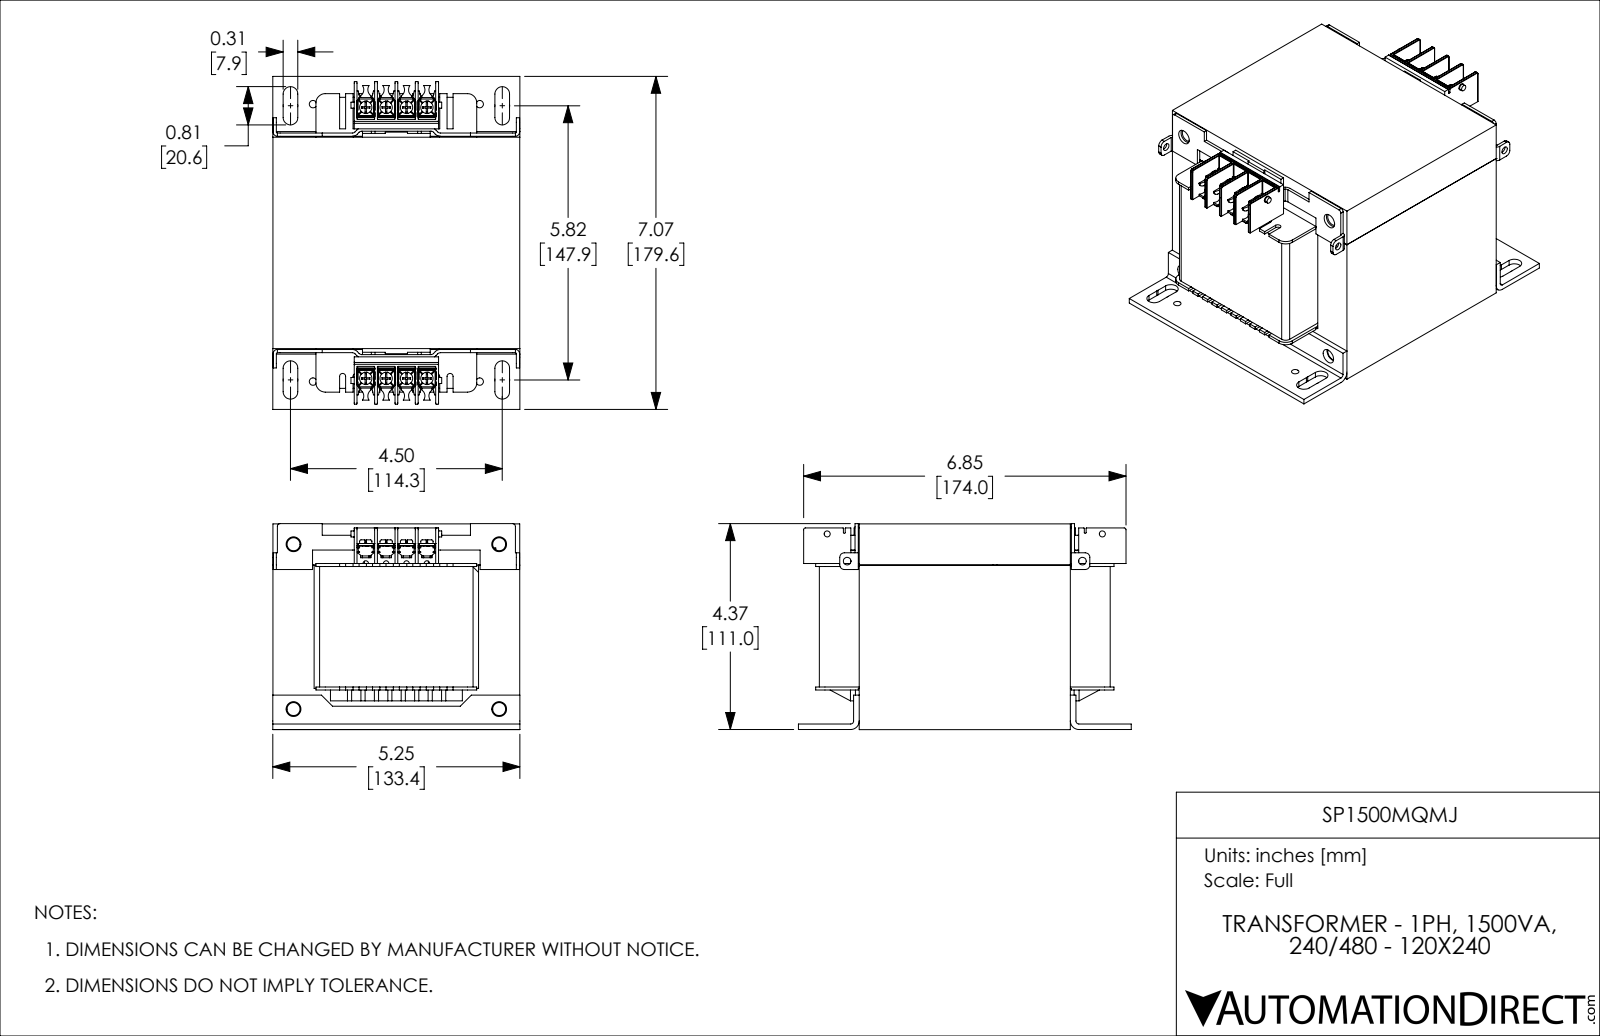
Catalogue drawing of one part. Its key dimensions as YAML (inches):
part_name: "SP1500MQMJ"
step_written_by: "SolidWorks 2018 (AUTOMOTIVE_DESIGN)"
units: inches
bodies: {solids: 42, faces: 3370, planar: 2121, cylindrical: 949, other: 300}
overall_size: [7.073, 5.25, 4.374]
volume: 116.8
surface_area: 453.4
round_holes:
  - {diameter: 0.157, count: 13}
  - {diameter: 0.105, count: 8}
  - {diameter: 0.138, count: 8}
  - {diameter: 0.276, count: 4}
  - {diameter: 0.315, count: 4}
  - {diameter: 0.161, count: 2}
  - {diameter: 0.177, count: 2}
round_bosses_or_shafts:
  - {diameter: 0.262, count: 8}
  - {diameter: 0.24, count: 8}
  - {diameter: 0.168, count: 8}
  - {diameter: 0.11, count: 8}
  - {diameter: 0.128, count: 2}
partial_cylinders:
  - {radius: 0.005, count: 52}
  - {radius: 0.01, count: 52}
  - {radius: 0.012, count: 38}
  - {radius: 0.029, count: 32}
  - {radius: 0.157, count: 20}
  - {radius: 0.035, count: 12}
  - {radius: 0.079, count: 10}
  - {radius: 0.065, count: 9}
face_to_face_distances: [0.874, 3.496, 4.37, 0.118, 1.748, 2.622, 0.992, 4.252, 1.707, 3.537]
hole_center_spacings: [0.433, 0.866, 5.762, 1.299, 5.746, 5.811, 5.752, 5.772]
